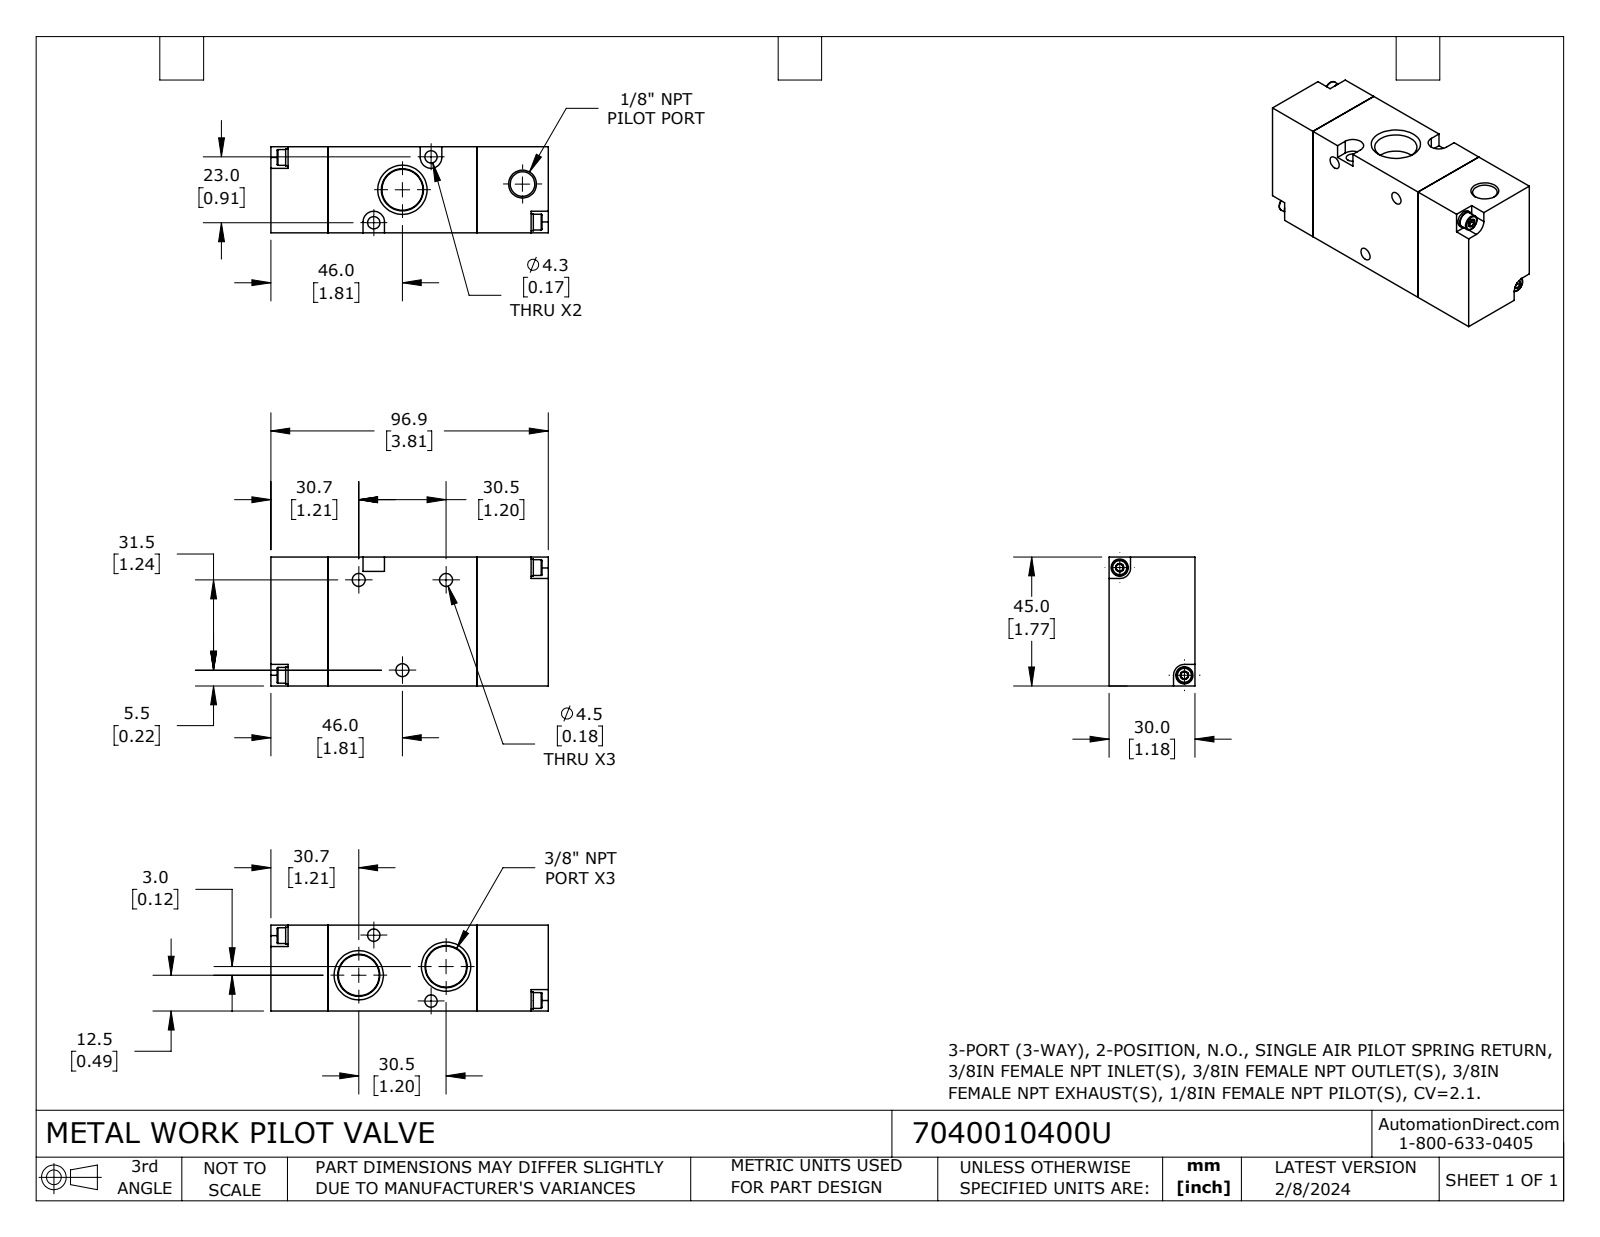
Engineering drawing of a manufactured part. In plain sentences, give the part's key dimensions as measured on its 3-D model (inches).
The part is named "7040010400U". Its 3-D file was written by "SolidWorks 2023 (CONFIG_CONTROL_DESIGN)". It is 11 solids with 229 faces: 108 planar, 51 cylindrical and 70 other. Overall it measures 3.815 by 1.772 by 1.181 inches. Its volume is 7.478 cubic inches and its surface area 42.2 square inches. Round holes: 4 of diameter 0.118, 3 of diameter 0.177, 2 of diameter 0.169, 1 of diameter 0.337. Round bosses or shafts: 4 of diameter 0.236, 4 of diameter 0.217. Partial cylindrical surfaces (rounded edges, fillets, slot ends): 3 of radius 0.15, 2 of radius 0.148, 1 of radius 0.146. The main face-to-face distances are 1.181, 2.043, 1.772, 0.787, 2.831, 3.815, 3.028, 0.984, 0.315, 1.457. The hole center spacings are 0.89, 1.378, 1.48, 1.727, 1.2, 1.201, 1.312, 2.113.
